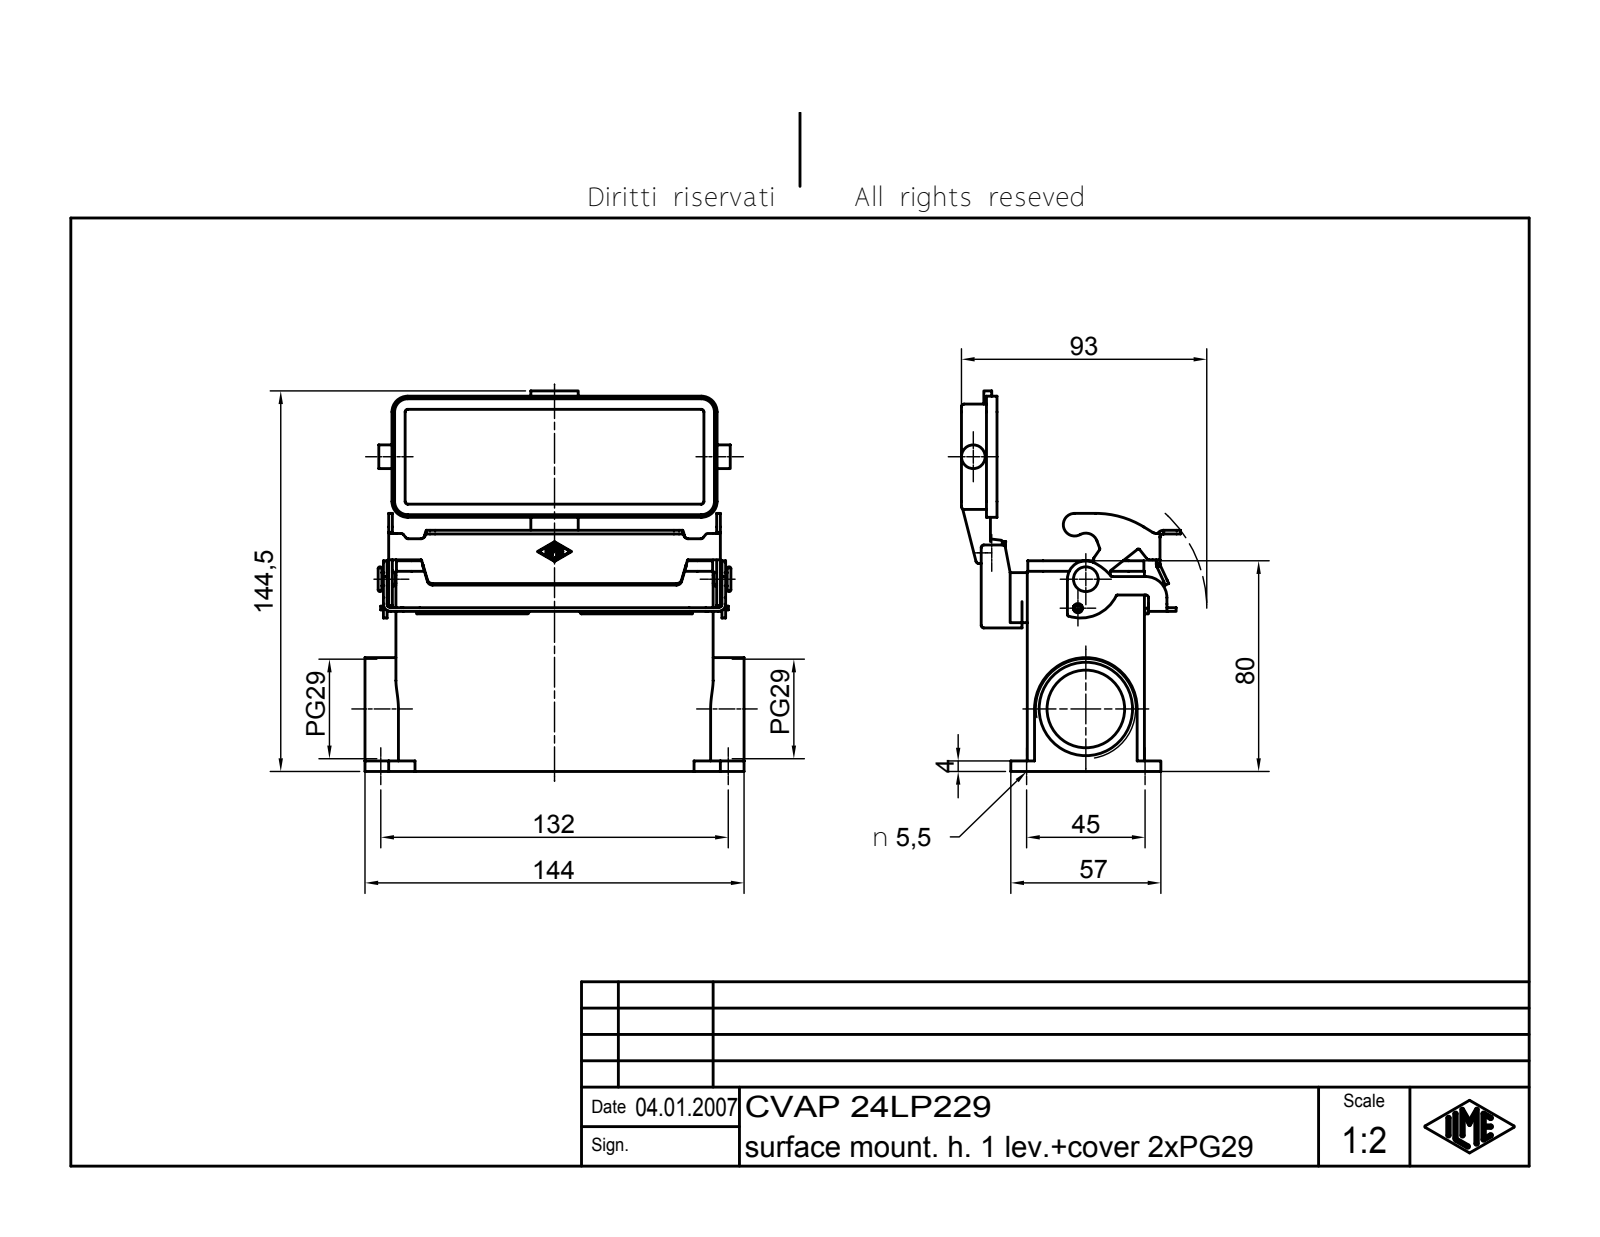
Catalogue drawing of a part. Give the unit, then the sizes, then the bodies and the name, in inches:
Units: inches
Overall size (bounding box): 5.689 × 5.669 × 3.277
Round holes (diameter × count): ⌀0.217 ×4, ⌀0.138 ×1, ⌀0.157 ×1, ⌀1.161 ×1, ⌀1.397 ×1
Round bosses / shafts (diameter × count): ⌀0.197 ×2, ⌀0.354 ×1, ⌀0.276 ×1, ⌀0.126 ×1, ⌀0.118 ×1
Partial cylindrical surfaces — rounded edges, fillets, slot ends (radius × count): R0.039 ×32, R0.01 ×15, R0.02 ×10, R0.059 ×9, R0.236 ×8, R0.079 ×7, R0.055 ×6, R0.11 ×6
Main face-to-face distances: 0.157, 1.594, 1.752, 1.437, 0.925, 0.079, 2.736, 1.142, 2.579, 0.984
Hole centre spacings: 1.772, 5.197, 5.491, 1.511
Volume: 10.86 in³ · Surface area: 163 in²
Bodies: 4 solids, 592 faces (232 planar, 195 cylindrical, 165 other)
Part name (STEP PRODUCT): CVAP 24LP229
STEP written by: Autodesk Inventor 7 (AUTOMOTIVE_DESIGN)
